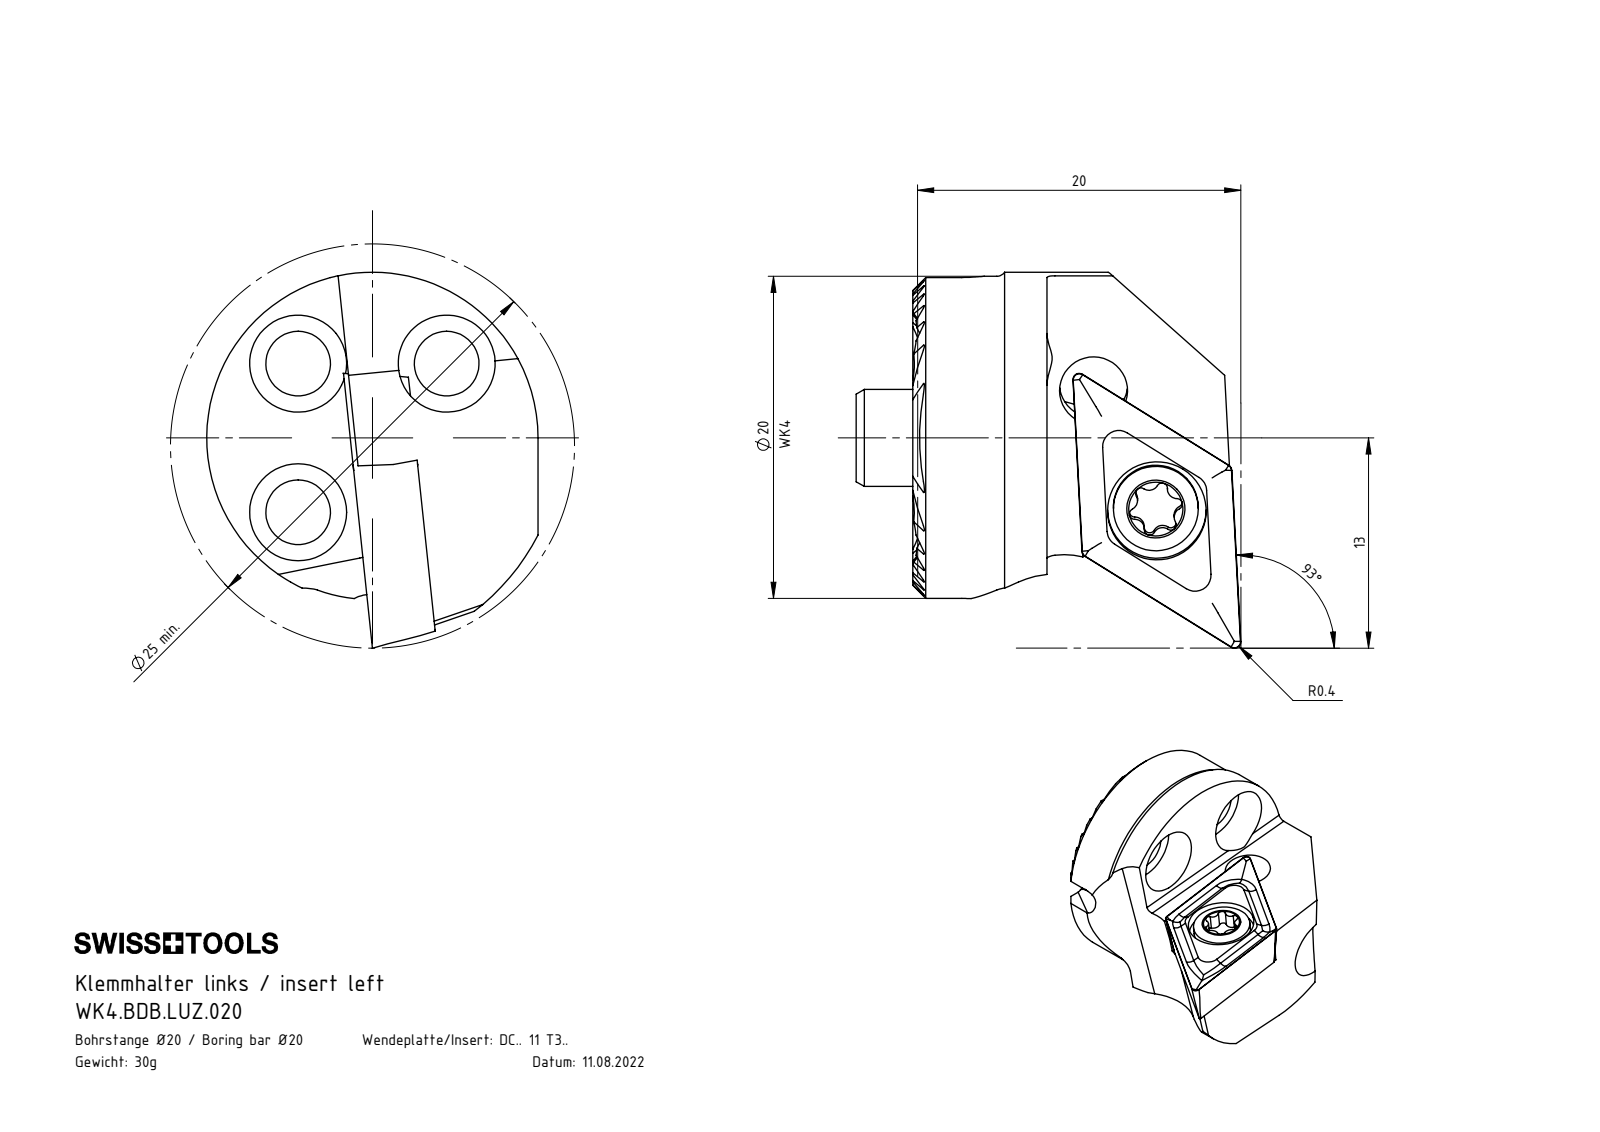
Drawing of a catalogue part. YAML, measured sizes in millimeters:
part_name: "WK4-BDB.LUZ.020_A; WK4.BDB.LUZ.020; WCB-ER2.001.009_A; DCMT11T304 (+1 more)"
step_written_by: "SolidWorks 2017 (AUTOMOTIVE_DESIGN)"
units: millimeters
bodies: {solids: 4, faces: 324, planar: 134, cylindrical: 118, other: 72}
overall_size: [23.8, 23.25, 20.5]
volume: 3505
surface_area: 3129
round_holes:
  - {diameter: 4, count: 3}
  - {diameter: 6, count: 3}
  - {diameter: 4.2, count: 2}
  - {diameter: 3.3, count: 1}
  - {diameter: 4.4, count: 1}
  - {diameter: 5.98, count: 1}
  - {diameter: 6.1, count: 1}
round_bosses_or_shafts:
  - {diameter: 20, count: 1}
  - {diameter: 6, count: 1}
  - {diameter: 5.25, count: 1}
  - {diameter: 4, count: 1}
partial_cylinders:
  - {radius: 0.12, count: 16}
  - {radius: 0.34, count: 6}
  - {radius: 0.59, count: 6}
  - {radius: 0.5, count: 1}
  - {radius: 5, count: 1}
  - {radius: 10.25, count: 1}
  - {radius: 14, count: 1}
face_to_face_distances: [4.33, 1.08, 3.25, 2.17, 5.41, 3.67, 8.66, 2.16, 3, 7.58]
hole_center_spacings: [6.51, 9.2, 8.29, 8.41, 13.01]
